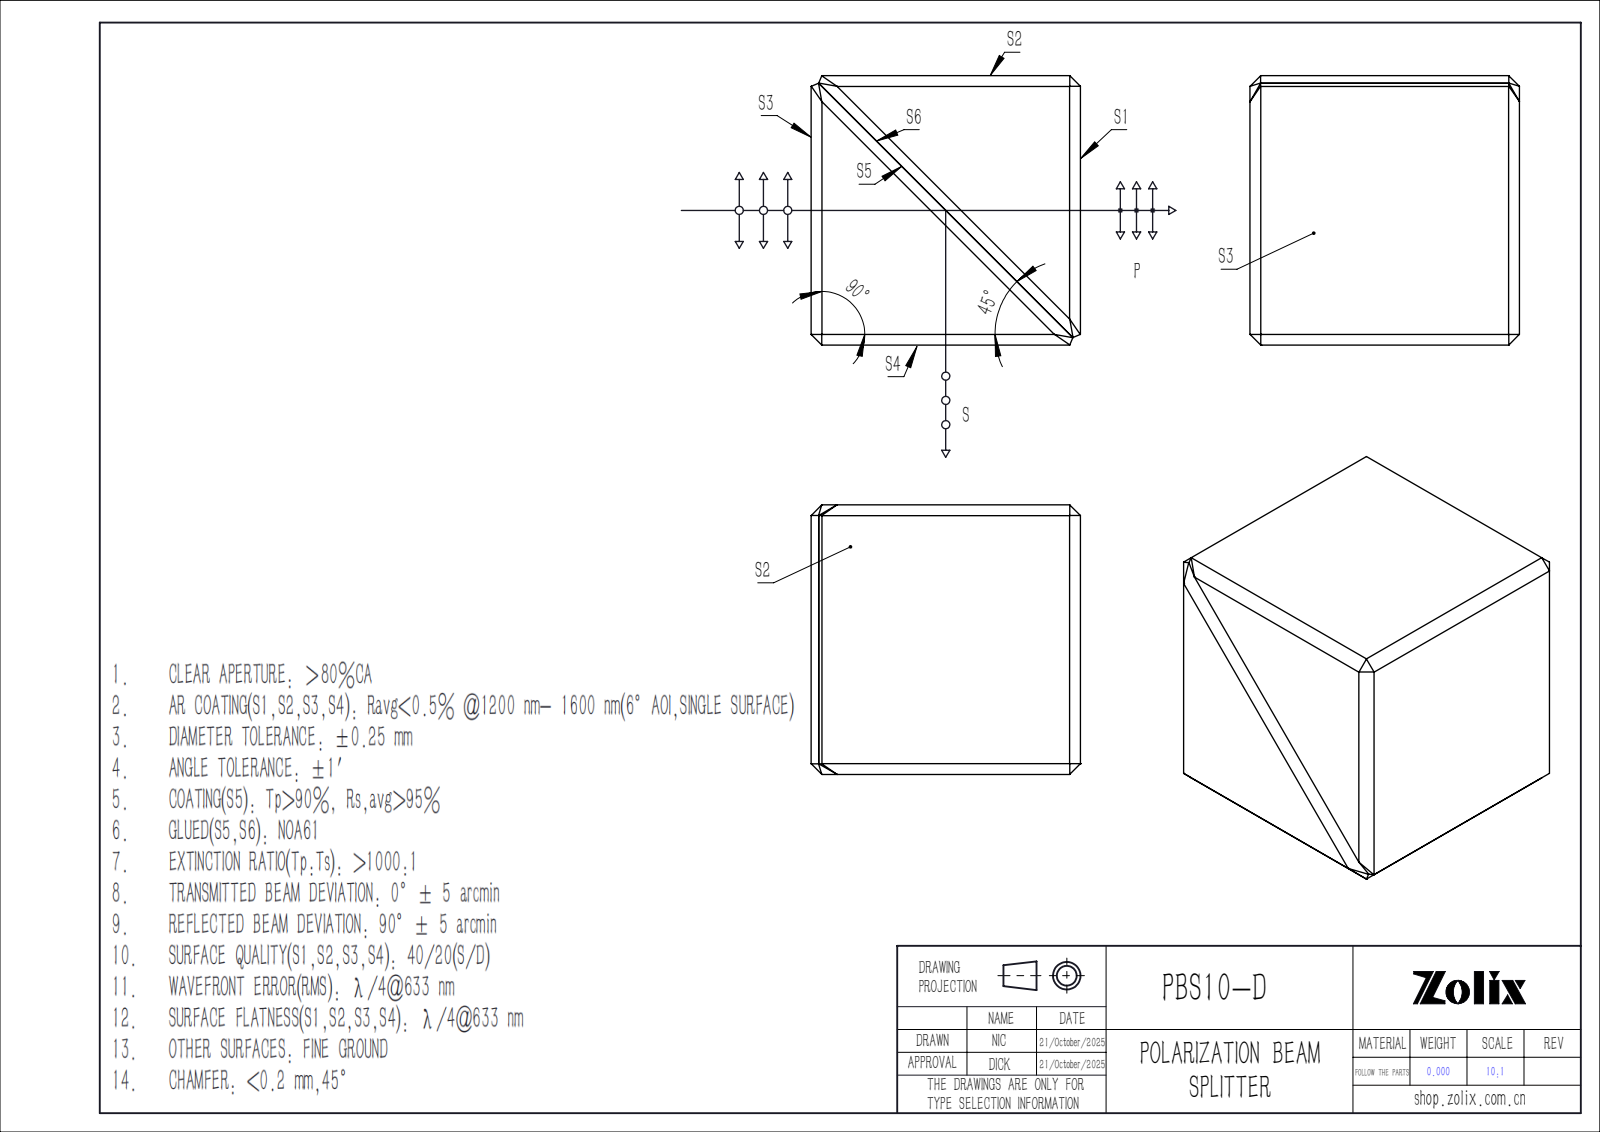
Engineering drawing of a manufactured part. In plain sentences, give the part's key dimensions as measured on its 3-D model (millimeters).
The part is named "PBS614-1-2; PBS614; PBS614-1-1". Its 3-D file was written by "SolidWorks 2022 (CONFIG_CONTROL_DESIGN)". It is 2 solids with 43 faces: 41 planar, 2 cylindrical and 0 other. Overall it measures 10 by 10 by 10 millimeters. Its volume is 996 cubic millimeters and its surface area 854 square millimeters. Round holes: 1 of diameter 0.2. The main face-to-face distances are 10, 13.86, 6.79, 12.7, 6.93, 6.92, 13.85, 14.7, 16.85, 14.69.
